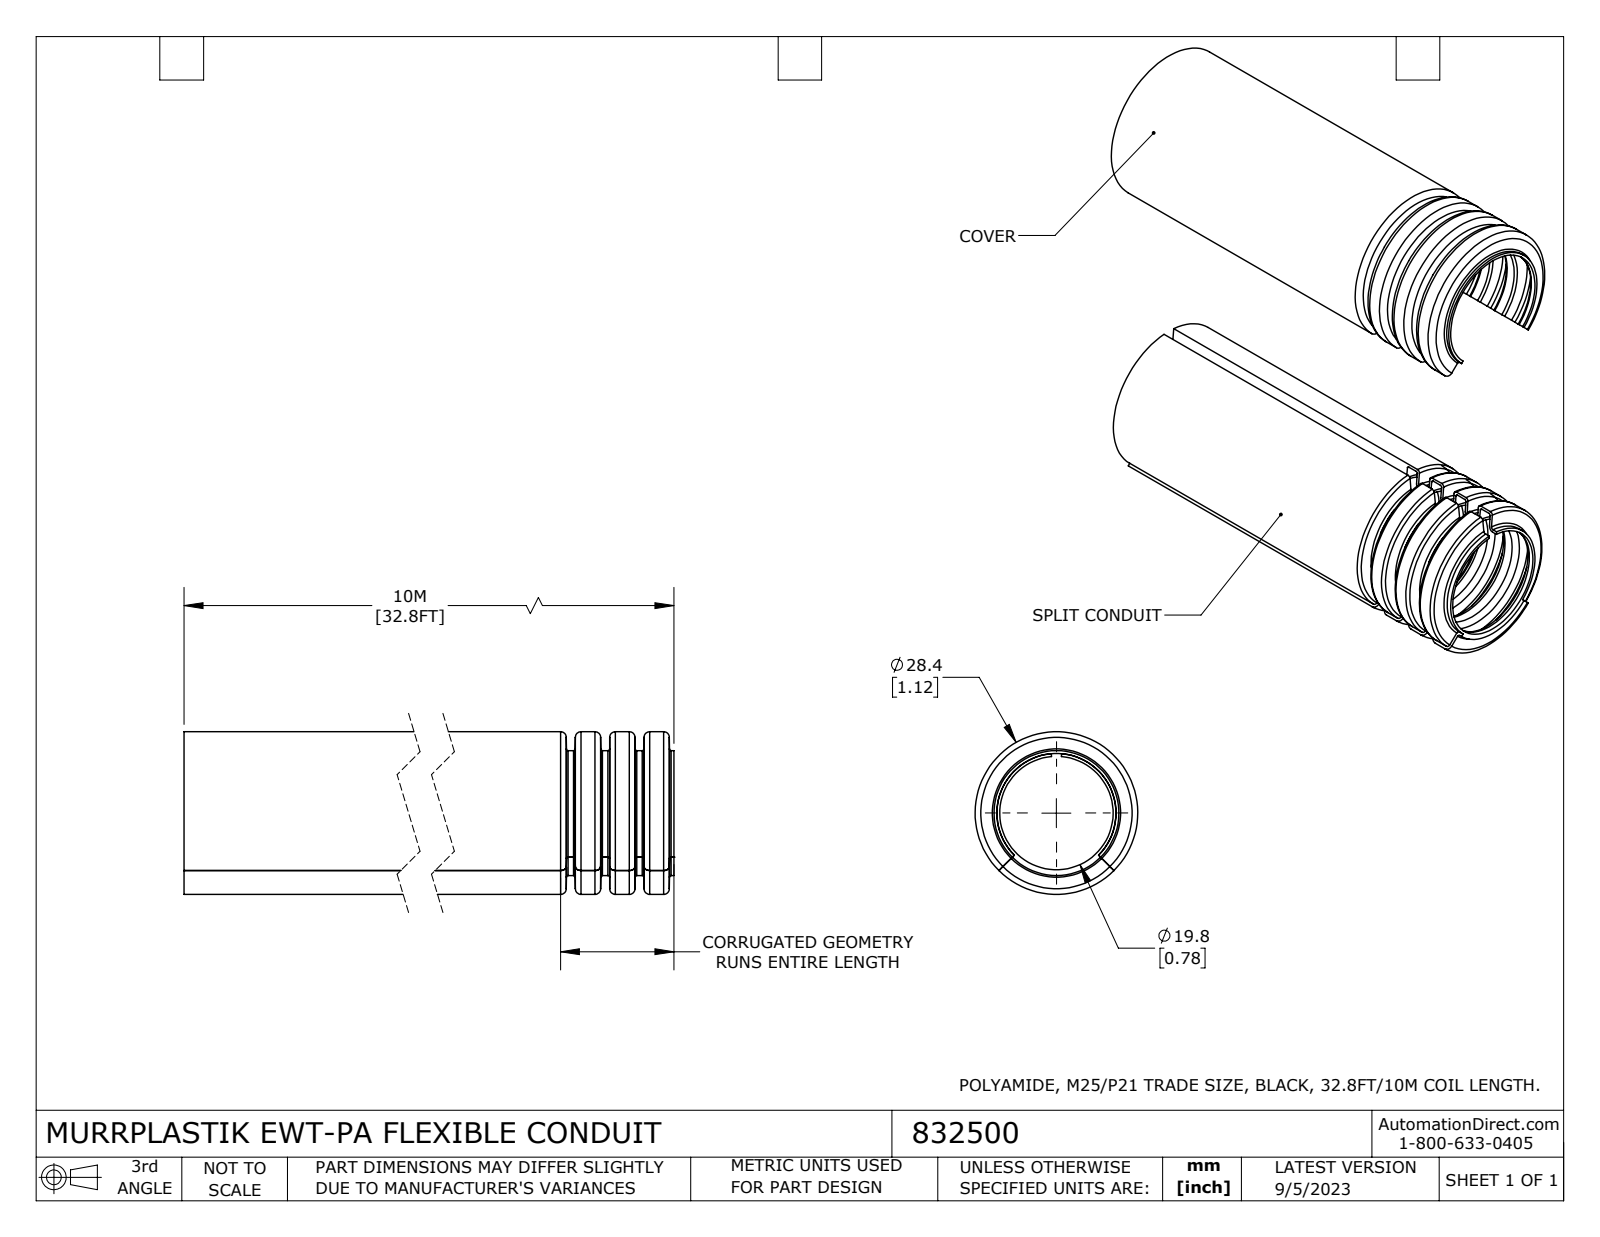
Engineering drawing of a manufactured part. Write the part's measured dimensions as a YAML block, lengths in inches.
part_name: "832500"
step_written_by: "SolidWorks 2021 (CONFIG_CONTROL_DESIGN)"
units: inches
bodies: {solids: 2, faces: 330, planar: 10, cylindrical: 107, other: 213}
overall_size: [3.15, 1.118, 1.118]
volume: 1.317
surface_area: 43.86
round_holes:
  - {diameter: 0.78, count: 1}
  - {diameter: 1.039, count: 1}
round_bosses_or_shafts:
  - {diameter: 1.118, count: 1}
  - {diameter: 0.858, count: 1}
partial_cylinders:
  - {radius: 0.409, count: 1}
  - {radius: 0.539, count: 1}
face_to_face_distances: [3.15]
